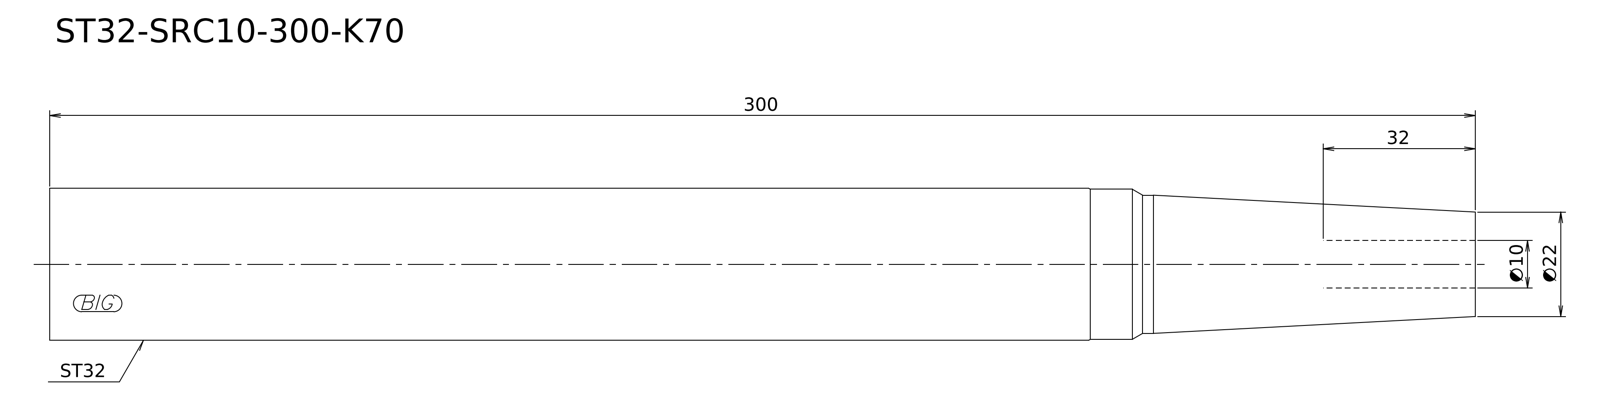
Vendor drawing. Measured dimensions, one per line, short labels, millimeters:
written by: Kubotek KeyCreator V8.5.1 (14335) (CONFIG_CONTROL_DESIGN)
unit: mm
bodies: 1 solid, 8 faces (2 planar, 3 cylindrical, 3 other)
size: 300 × 32 × 32
volume: 221 081 mm³; area: 29 973 mm²
bosses: 1× ⌀32, 1× ⌀31.6, 1× ⌀29.1
face distances: 300
